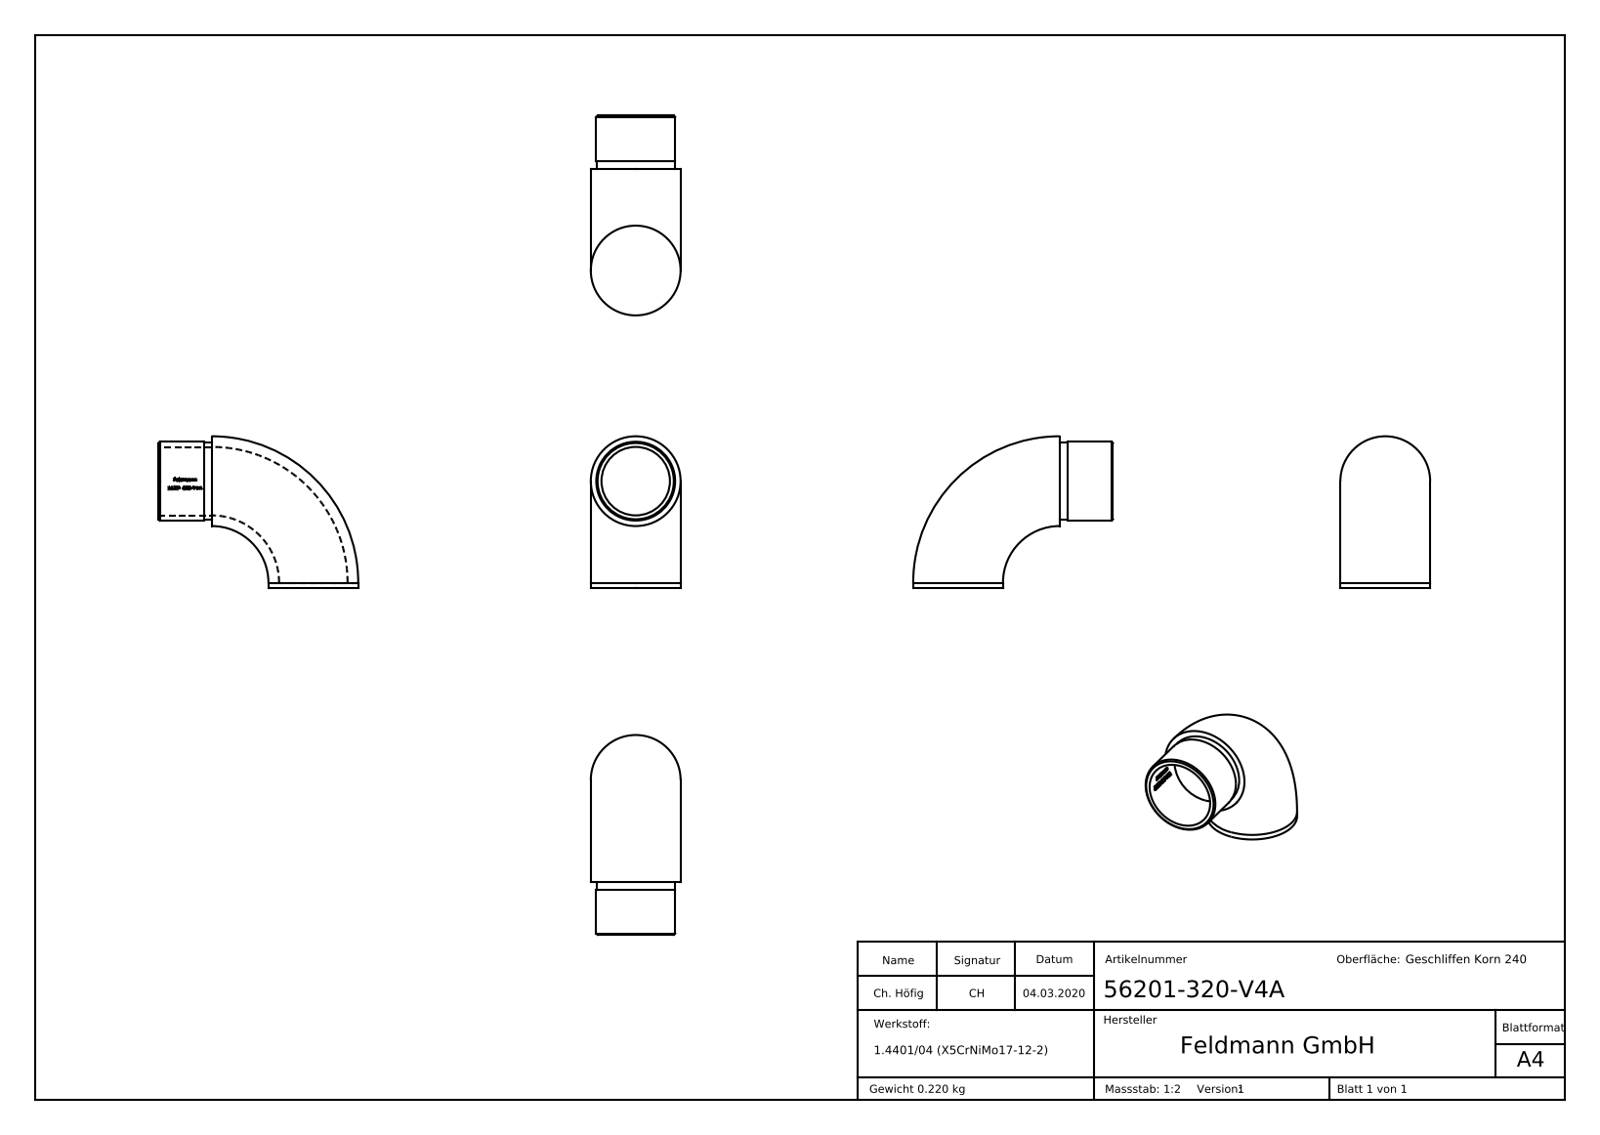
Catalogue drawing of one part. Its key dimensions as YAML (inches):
part_name: "56201-320-V4A"
step_written_by: "SolidWorks 2015 (CONFIG_CONTROL_DESIGN)"
units: inches
bodies: {solids: 1, faces: 273, planar: 128, cylindrical: 33, other: 112}
overall_size: [2.953, 2.244, 1.327]
volume: 1.676
surface_area: 25.84
round_holes:
  - {diameter: 1.012, count: 1}
round_bosses_or_shafts:
  - {diameter: 1.327, count: 1}
  - {diameter: 1.165, count: 1}
  - {diameter: 1.15, count: 1}
partial_cylinders:
  - {radius: 0.51, count: 1}
face_to_face_distances: [0.079, 0.787, 0.118, 0.669, 0.015, 0.052, 0.054, 0.132, 0.017, 0.09]
